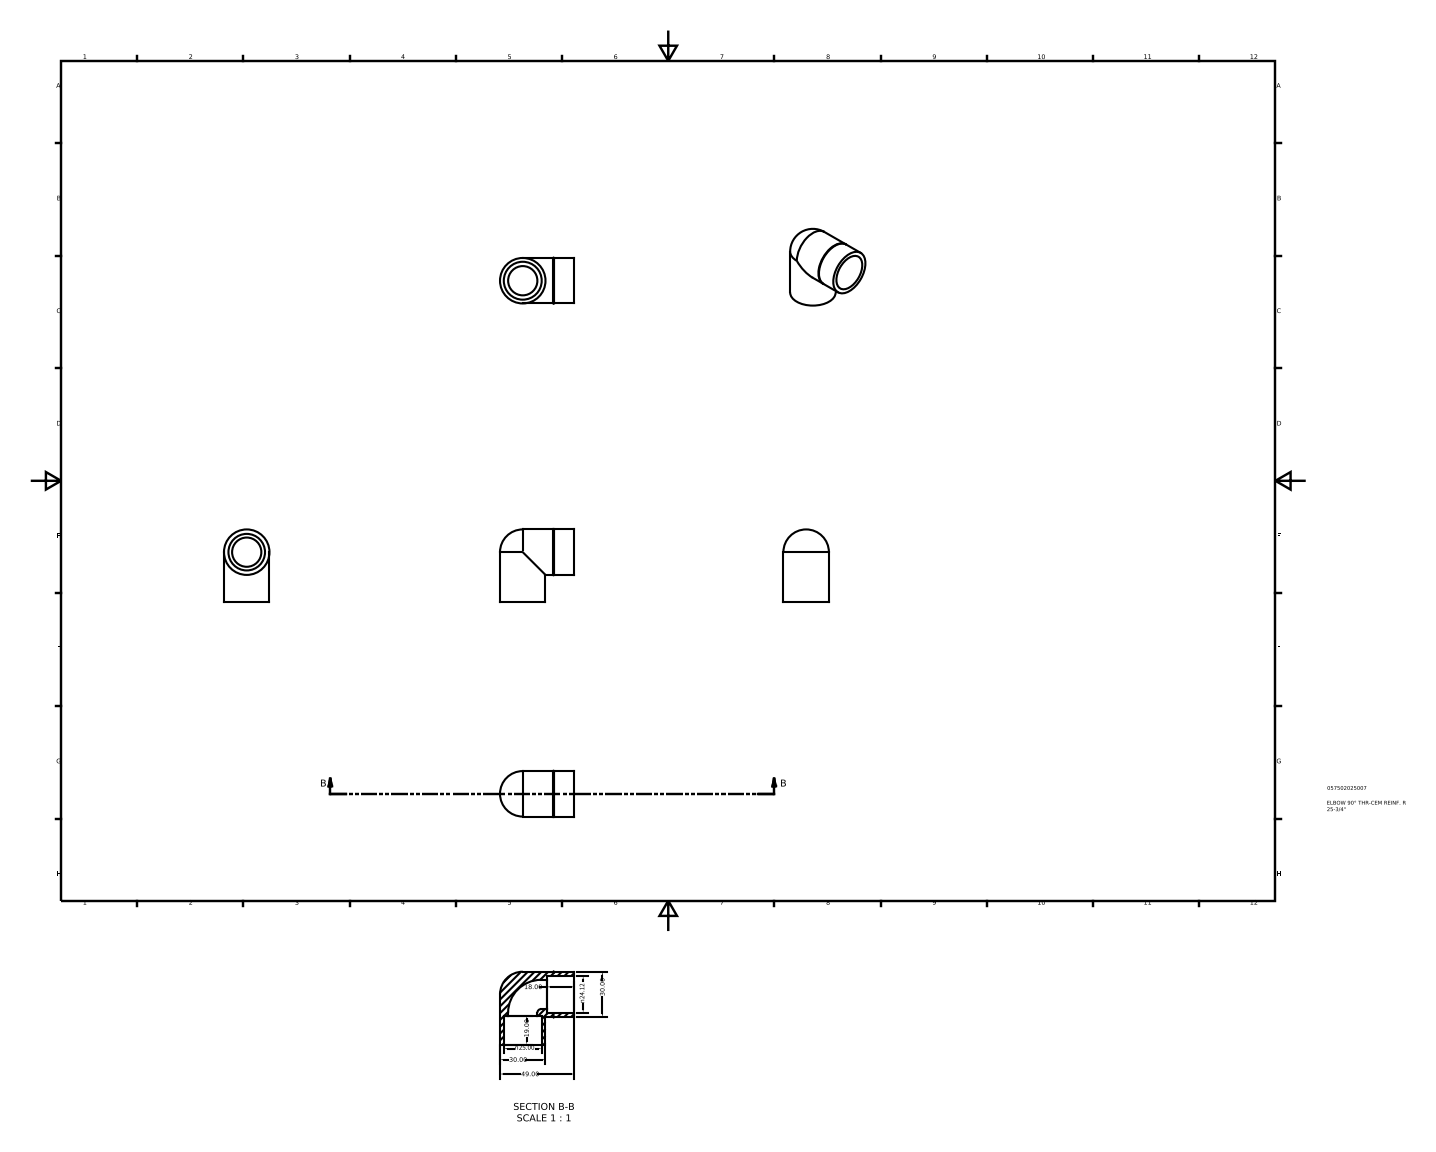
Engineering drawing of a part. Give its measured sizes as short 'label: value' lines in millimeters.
name: 057502025007
written by: Autodesk Inventor 2015 (AUTOMOTIVE_DESIGN)
unit: mm
bodies: 1 solid, 15 faces (4 planar, 7 cylindrical, 4 other)
size: 49 × 48 × 30
volume: 21 575 mm³; area: 11 368 mm²
holes: 2× ⌀19.29, 1× ⌀24.12, 1× ⌀25
bosses: 2× ⌀30
face distances: 19, 18
